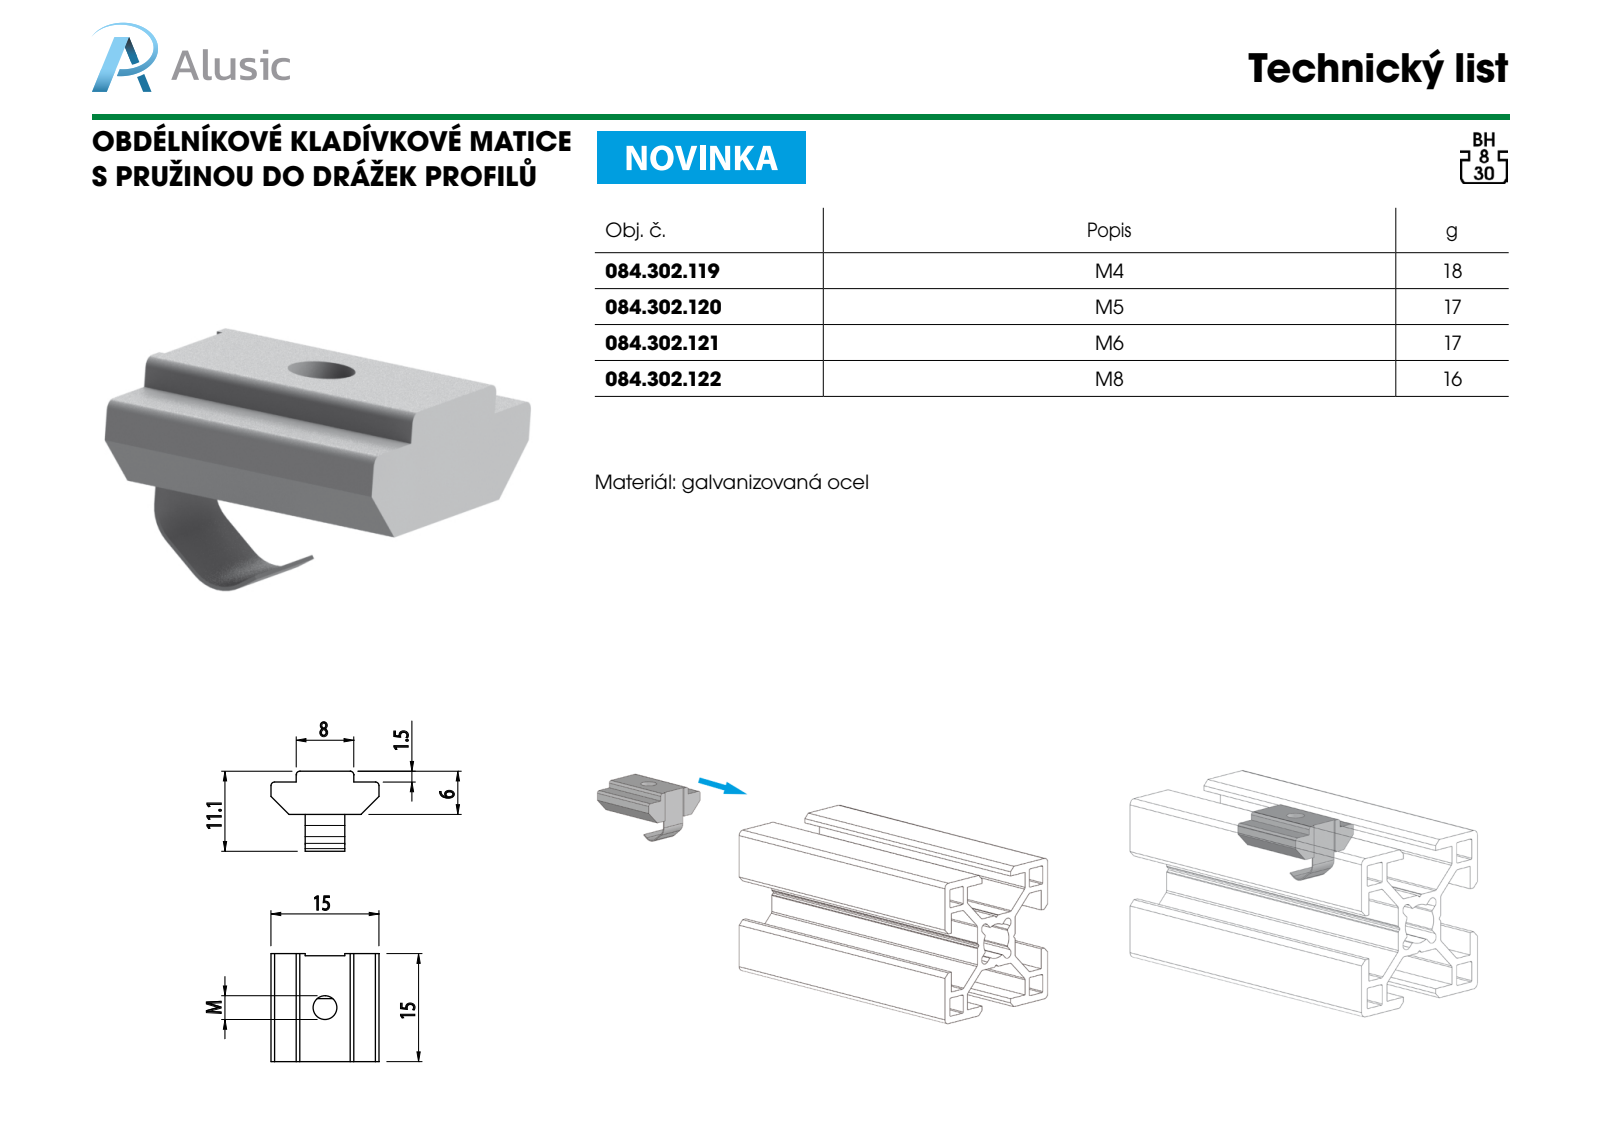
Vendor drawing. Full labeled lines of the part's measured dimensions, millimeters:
Part name (STEP PRODUCT): 084.302.121
STEP written by: SolidWorks 2016 (CONFIG_CONTROL_DESIGN)
Units: millimetres
Bodies: 1 solid, 34 faces (24 planar, 10 cylindrical, 0 other)
Overall size (bounding box): 15 × 15 × 11.1
Volume: 978 mm³ · Surface area: 883 mm²
Round holes (diameter × count): ⌀5 ×1
Partial cylindrical surfaces — rounded edges, fillets, slot ends (radius × count): R0.5 ×4, R2 ×2, R2.2 ×2
Main face-to-face distances: 4.5, 6, 1.5, 15, 14.7, 3.5, 11.5, 8, 0.5, 14.5
